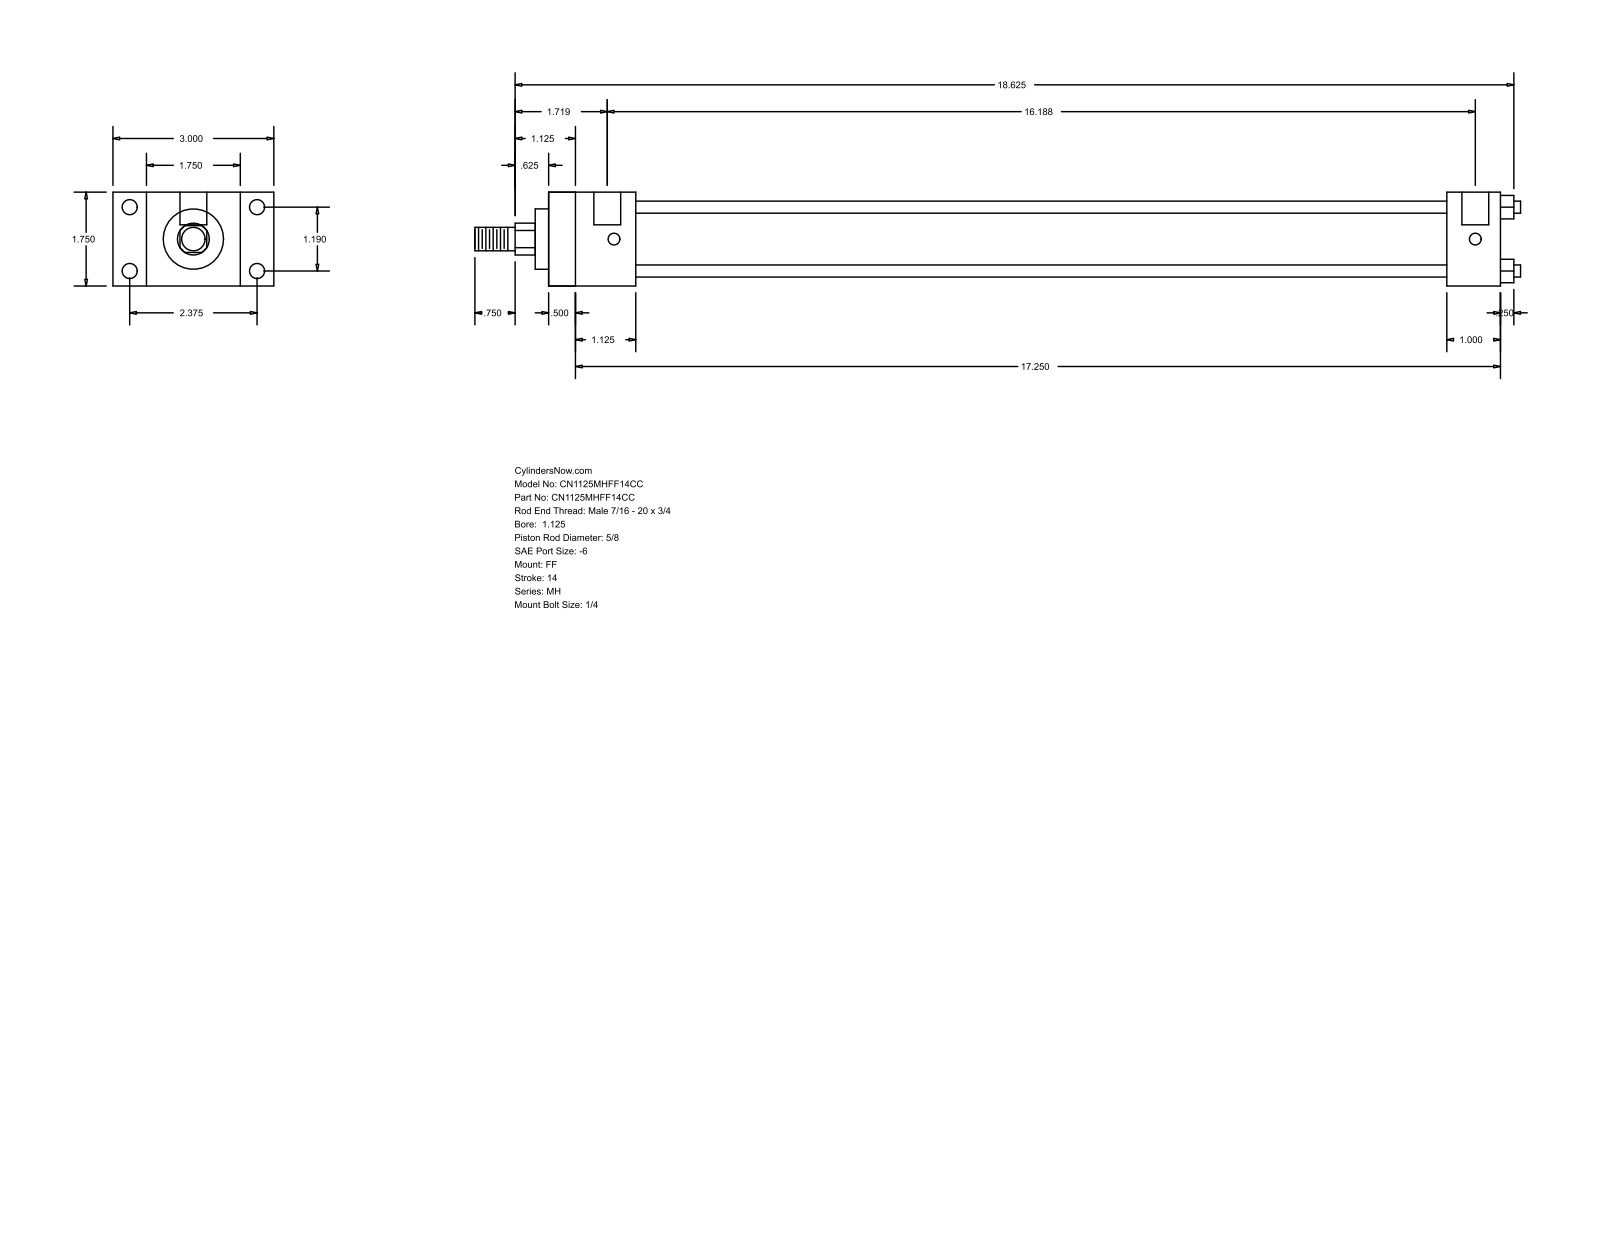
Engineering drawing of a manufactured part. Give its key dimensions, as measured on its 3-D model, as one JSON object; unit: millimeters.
{"part_name": "MH_FF__0112_0.625", "step_written_by": "GSSL Pune (CONFIG_CONTROL_DESIGN)", "units": "millimeters", "bodies": {"solids": 0, "faces": 92, "planar": 64, "cylindrical": 28, "other": 0}, "overall_size": [495.3, 76.2, 44.45], "round_holes": [[5.56, 4], [7.14, 4], [12.7, 2]], "round_bosses_or_shafts": [[5.71, 4], [34.92, 1], [28.57, 1], [15.88, 1], [11.11, 1]], "partial_cylinders_radius": [[7.54, 1]], "face_to_face_distances": [44.46, 450.85, 12.69, 438.16, 15.87, 28.58, 60.33, 41.27, 425.44, 412.75], "hole_center_spacings": [30.22, 60.32, 67.47, 407.99, 3.17, 411.16]}
